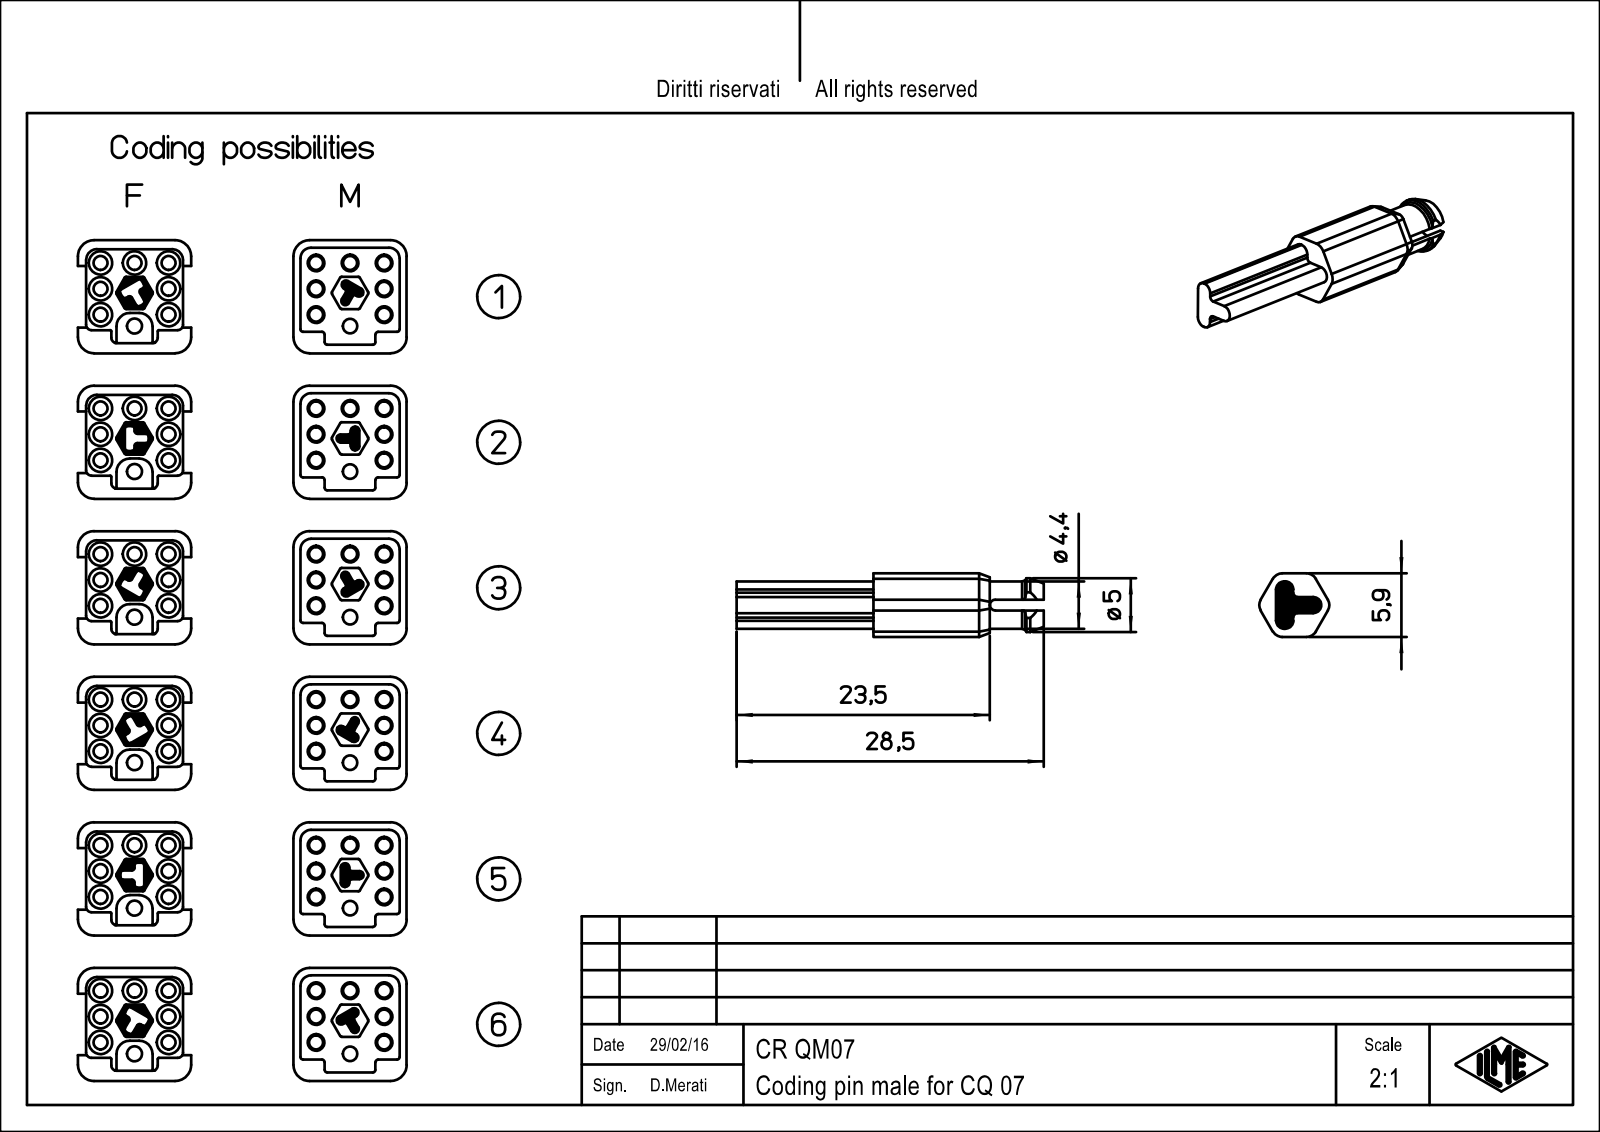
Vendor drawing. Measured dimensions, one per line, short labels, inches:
name: CR_QM07
written by: PTC Creo Elements/Direct Modeling 19.0B 21-Mar-2015 (C) Parametric Technology GmbH (AUTOMOTIVE_DESIGN)
unit: in
bodies: 1 solid, 24 faces (18 planar, 4 cylindrical, 2 other)
size: 1.122 × 0.268 × 0.232
volume: 0.034 in³; area: 0.896 in²
bosses: 1× ⌀0.197, 1× ⌀0.173
face distances: 0.232, 0.087, 0.146, 0.03, 0.203, 0.057, 0.116, 0.063, 0.059, 0.173
